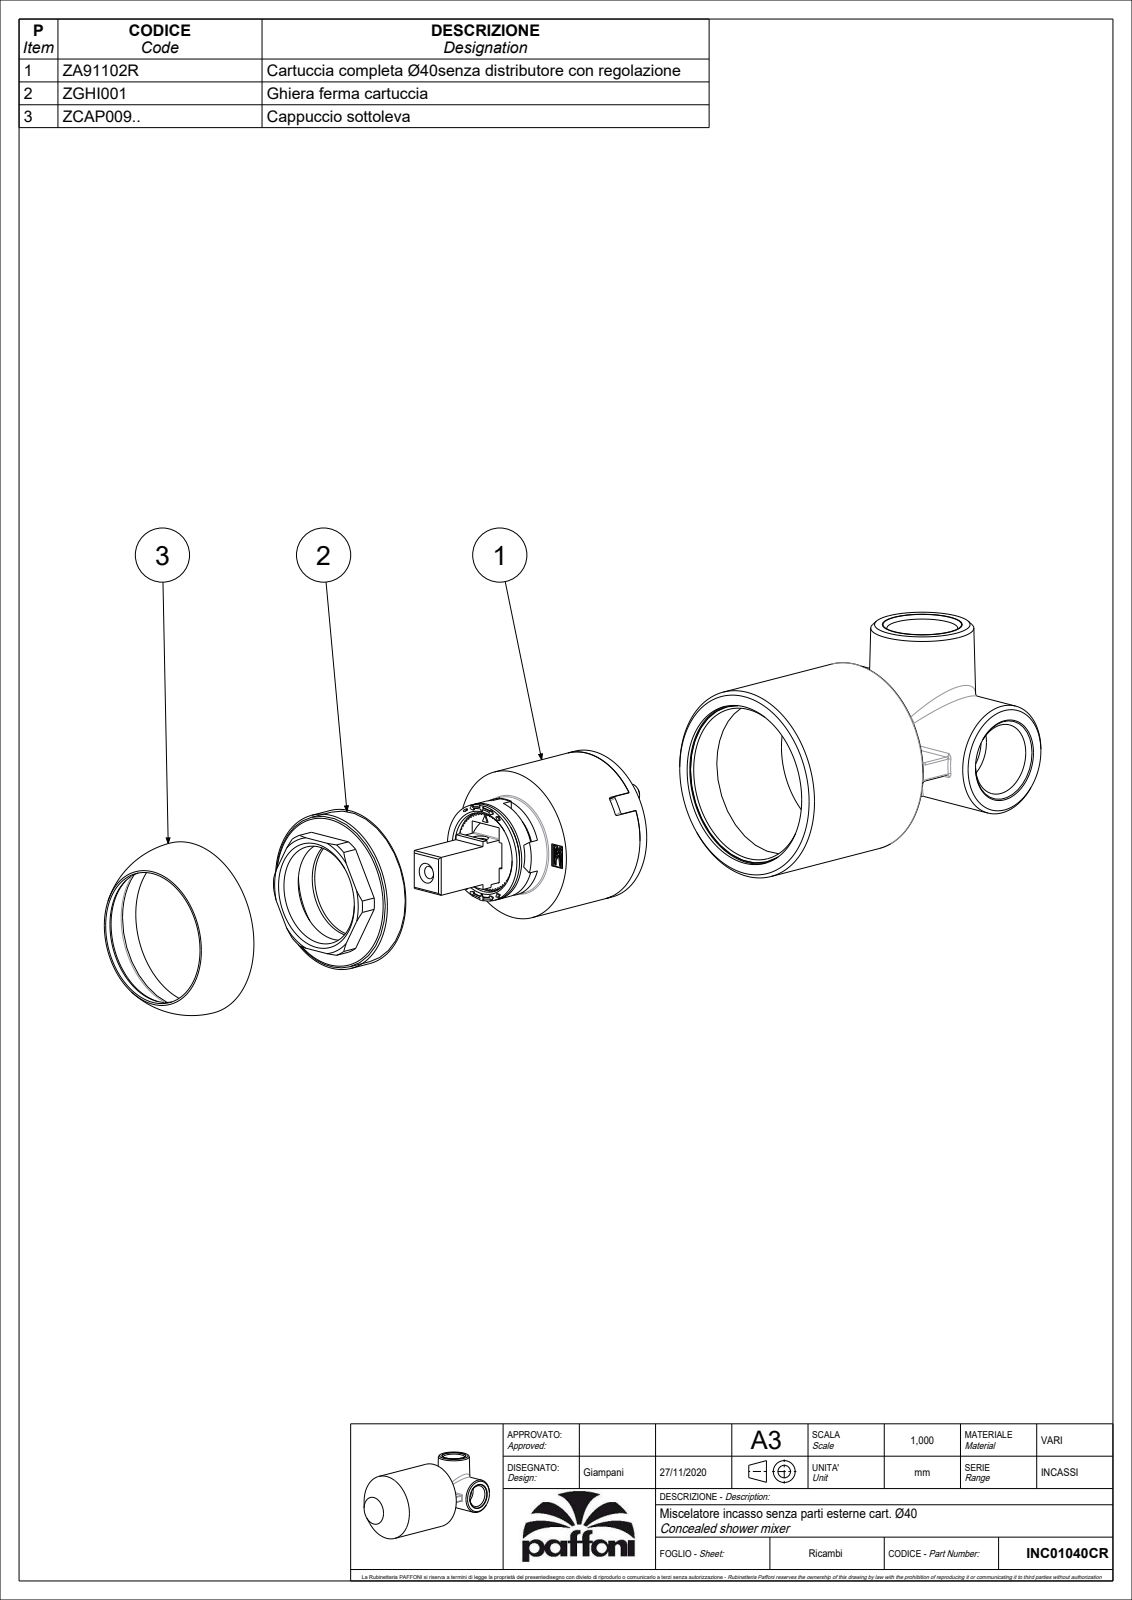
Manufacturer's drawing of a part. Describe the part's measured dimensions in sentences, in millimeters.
The part is named "INC01040CR". Its 3-D file was written by "CREO PARAMETRIC BY PTC INC, 2020044 (CONFIG_CONTROL_DESIGN)". It is 2 solids with 909 faces: 474 planar, 239 cylindrical and 196 other. Overall it measures 111.5 by 61 by 59.1 millimeters. Its volume is 133 908 cubic millimeters and its surface area 75 667 square millimeters. Round holes: 5 of diameter 8, 2 of diameter 3.3, 2 of diameter 11.7, 1 of diameter 3, 1 of diameter 4, 1 of diameter 5, 1 of diameter 9, 1 of diameter 11, 1 of diameter 11.6, 1 of diameter 16, 1 of diameter 18.6, 1 of diameter 19. Round bosses or shafts: 1 of diameter 56, 1 of diameter 50, 1 of diameter 39.5, 1 of diameter 36.7, 1 of diameter 33, 1 of diameter 29, 1 of diameter 25.8, 1 of diameter 25.75. Partial cylindrical surfaces (rounded edges, fillets, slot ends): 26 of radius 0.5, 24 of radius 0.2, 6 of radius 1, 2 of radius 12, 1 of radius 3.5, 1 of radius 7, 1 of radius 10.05, 1 of radius 11.9. The main face-to-face distances are 40, 21.4, 18.3, 3.1, 37.5, 1, 0.5, 34, 35.5, 7. The hole center spacings are 0.54, 1.51, 2, 7.77, 8.6, 8.7, 8.83, 9.7.
